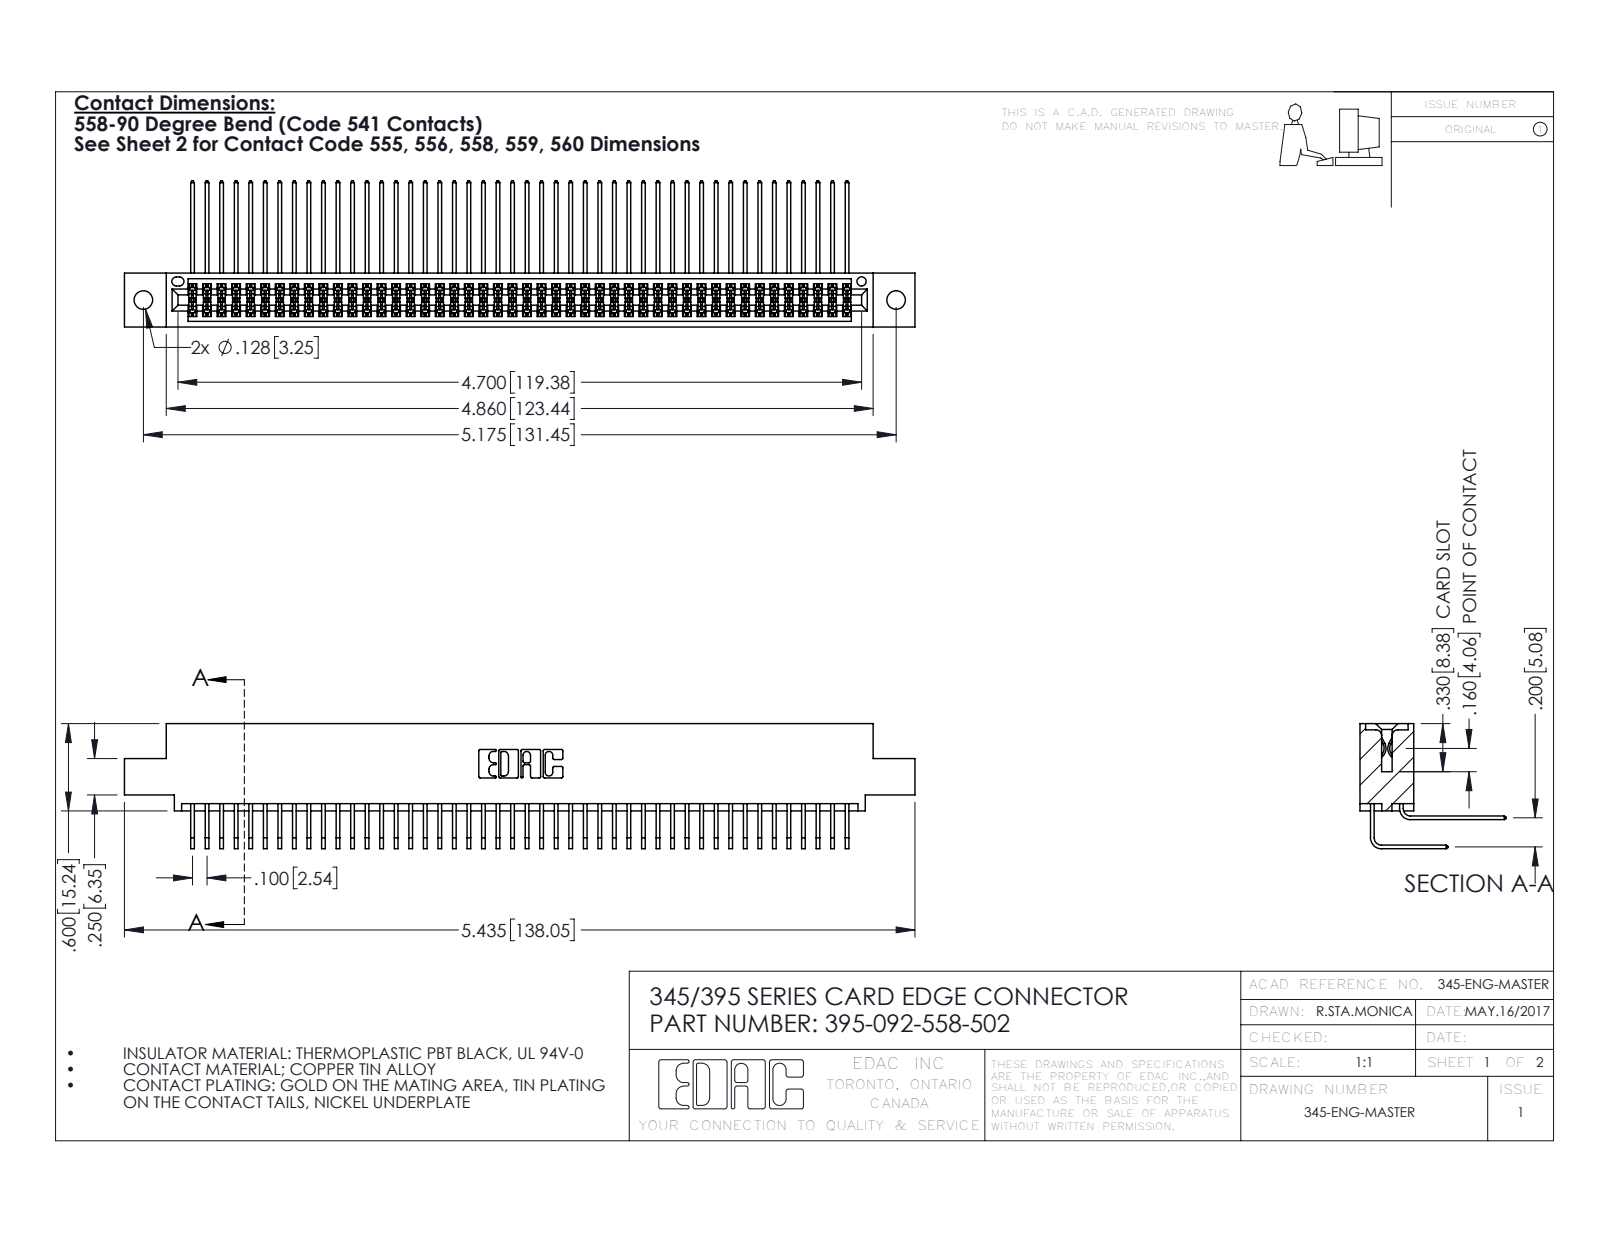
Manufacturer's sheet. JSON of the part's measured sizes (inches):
{"part_name": "395-092-558-502; 345 Part_0.110 Offset - 0.128 Dia; 345-292-001_558 559 Tail - 1; 345-292-001_558 Tail - 2", "step_written_by": "SolidWorks 2016 (CONFIG_CONTROL_DESIGN)", "units": "inches", "bodies": {"solids": 93, "faces": 4914, "planar": 3304, "cylindrical": 1610, "other": 0}, "overall_size": [5.435, 1.005, 0.859], "volume_in3": 0.846, "surface_area_in2": 35.48, "round_holes": [[0.128, 2], [0.064, 1]], "partial_cylinders_radius": [[0.006, 139], [0.01, 22], [0.007, 6], [0.031, 6], [0.026, 3], [0.014, 2], [0.019, 2], [0.022, 2]], "face_to_face_distances": [0.072, 0.298, 0.2, 0.37, 0.098, 0.272, 0.025, 0.225, 0.025, 0.175], "hole_center_spacings": [0.27, 4.939, 5.175]}
